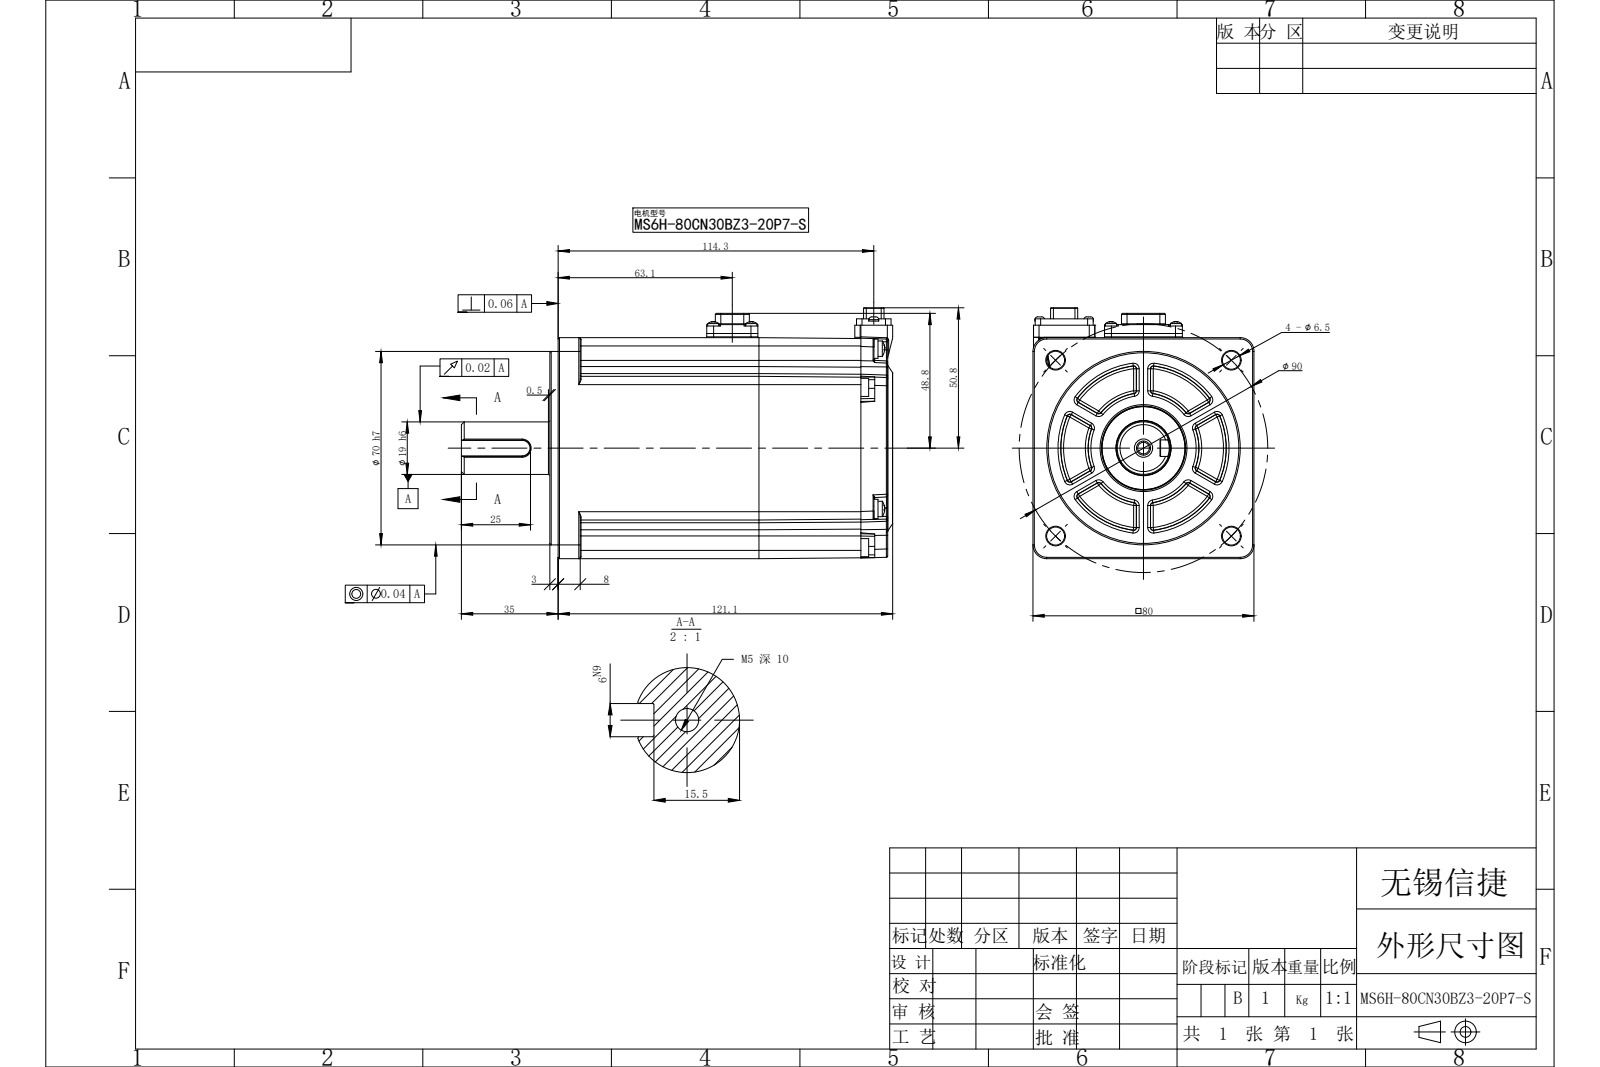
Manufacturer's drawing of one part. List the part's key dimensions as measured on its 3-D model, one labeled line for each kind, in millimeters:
Part name (STEP PRODUCT): MS6H-80CN30BZ3-20P7-S
STEP written by: SolidWorks 2022 (CONFIG_CONTROL_DESIGN)
Units: millimetres
Bodies: 0 solids, 1008 faces (382 planar, 287 cylindrical, 339 other)
Overall size (bounding box): 156.1 × 90.8 × 80
Round holes (diameter × count): ⌀2.1 ×4, ⌀6.5 ×4, ⌀1.6 ×2, ⌀4.2 ×1, ⌀20 ×1
Round bosses / shafts (diameter × count): ⌀7 ×4, ⌀6.53 ×4, ⌀5.6 ×4, ⌀4 ×4, ⌀3.5 ×2, ⌀70 ×1, ⌀30 ×1, ⌀19.8 ×1
Partial cylindrical surfaces — rounded edges, fillets, slot ends (radius × count): R0.3 ×39, R0.5 ×37, R3 ×29, R1 ×25, R0.2 ×23, R2 ×12, R0.6 ×4, R2.15 ×4
Main face-to-face distances: 80, 14, 1.8, 66, 119.3, 121.1, 9.7, 109.6, 11.5, 3
Hole centre spacings: 45, 63.64, 8, 16.6, 18.43, 90, 23.5, 47.99
